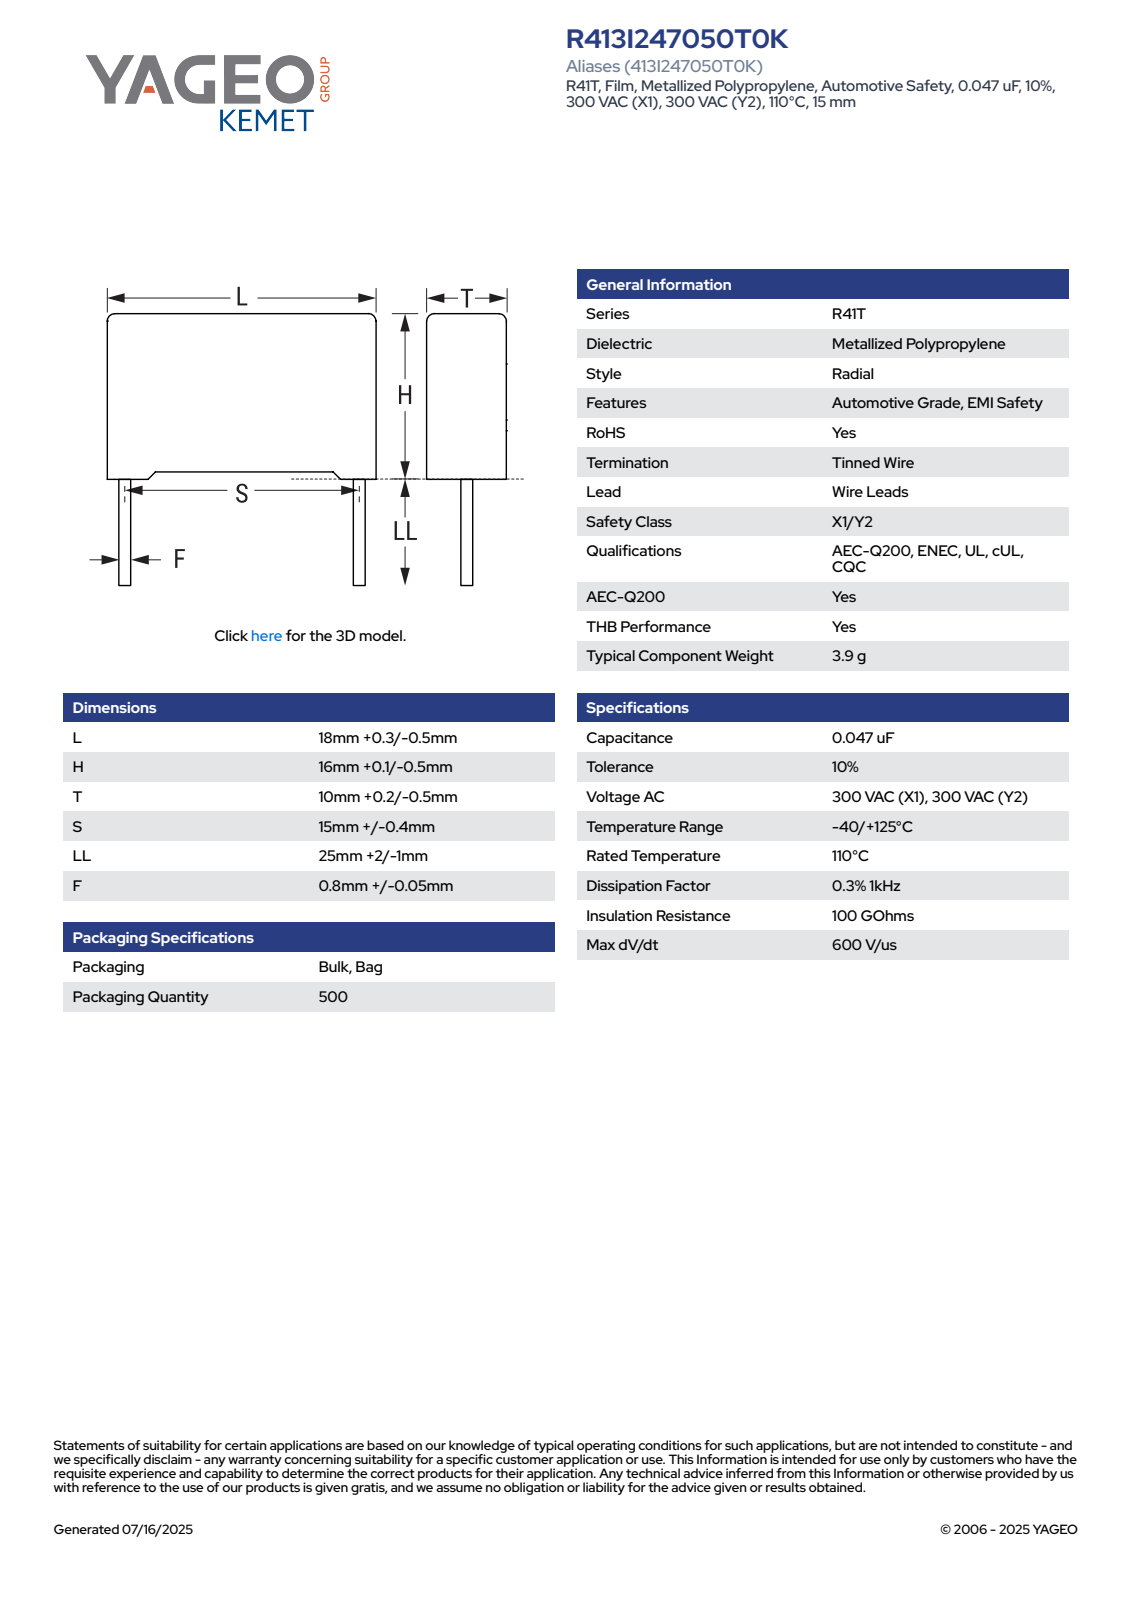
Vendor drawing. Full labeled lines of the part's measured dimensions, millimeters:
Part name (STEP PRODUCT): CFR_RB2_18X16X10_L18.3H16.1T10.2S15LL27F0.85
STEP written by: SolidWorks 2021 (AUTOMOTIVE_DESIGN)
Units: millimetres
Bodies: 4 solids, 85 faces (77 planar, 8 cylindrical, 0 other)
Overall size (bounding box): 43.1 × 18.3 × 10.21
Volume: 2 911 mm³ · Surface area: 1 466 mm²
Round bosses / shafts (diameter × count): ⌀0.85 ×2
Partial cylindrical surfaces — rounded edges, fillets, slot ends (radius × count): R0.5 ×4
Main face-to-face distances: 10.2, 18.3, 15.35, 0.61, 0.75, 16.1, 17.69, 0.56, 15.54, 9.59
